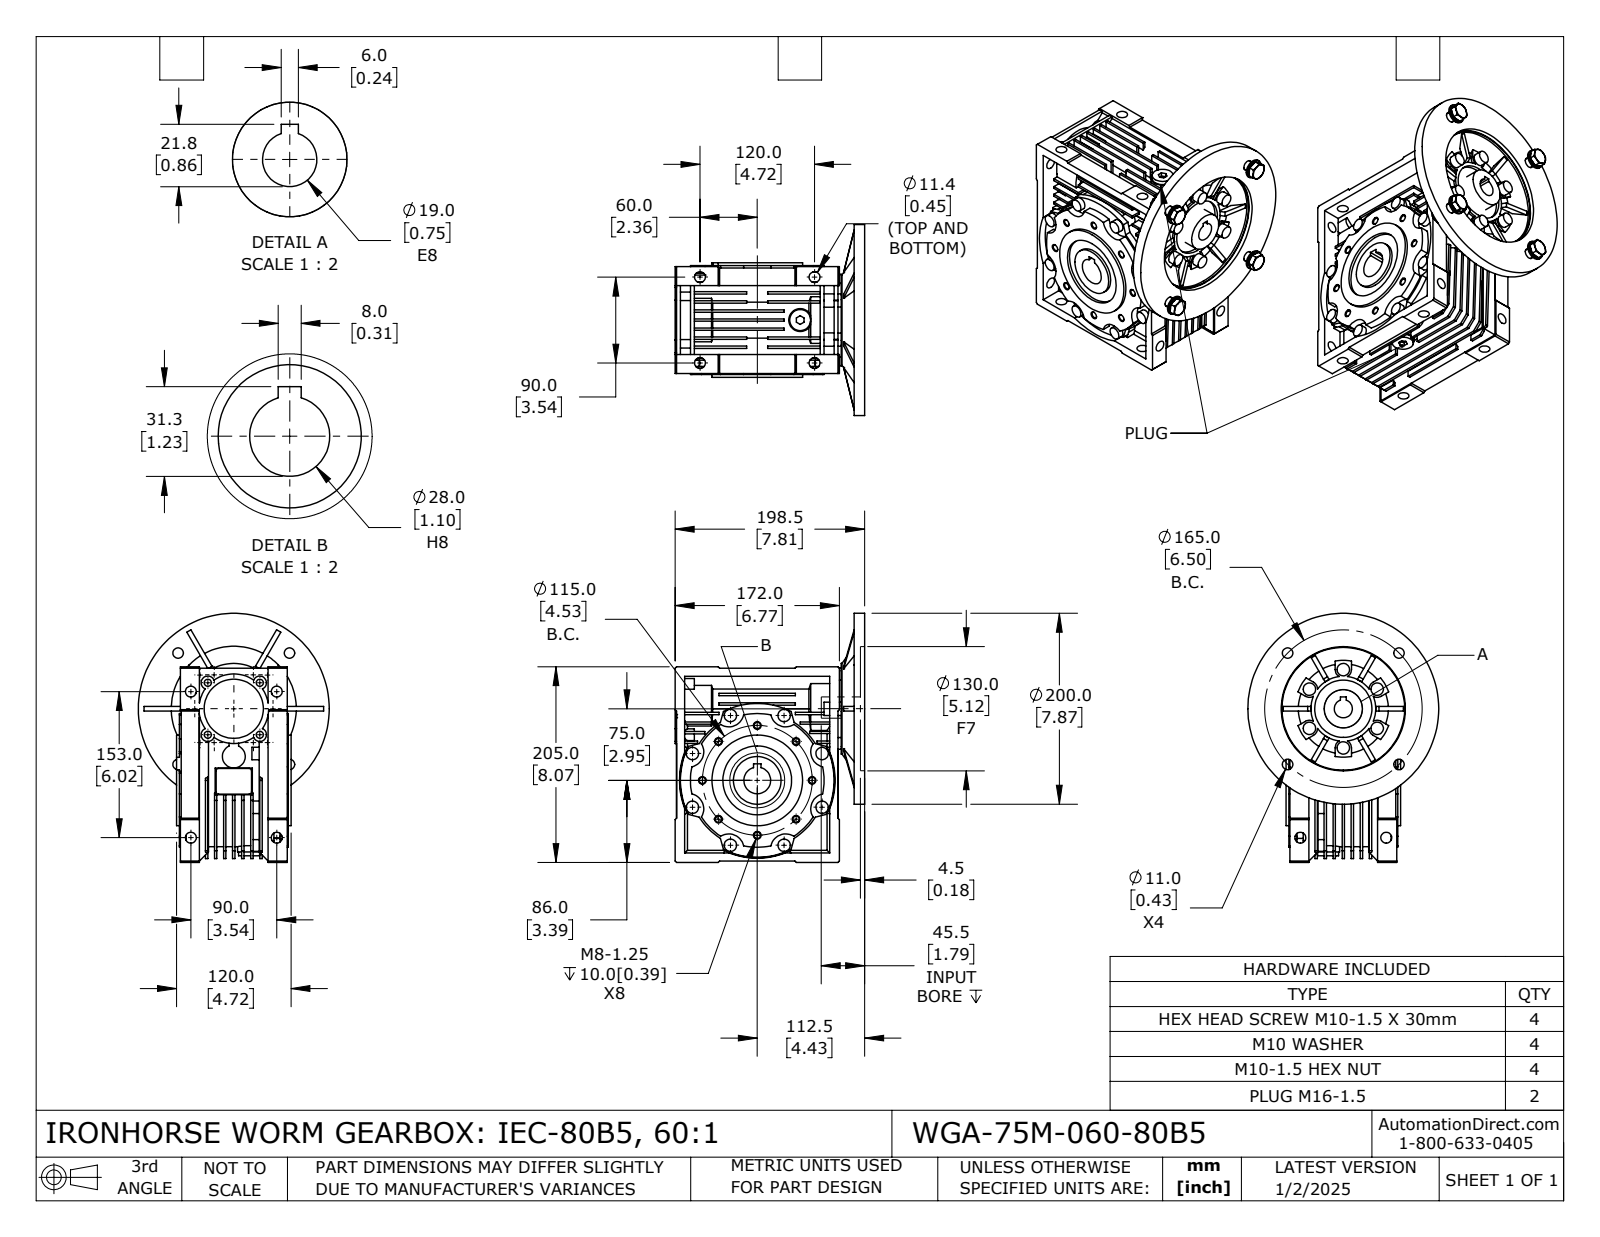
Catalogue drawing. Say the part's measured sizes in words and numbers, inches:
The part is named "WGA-75M-060-80B5". Its 3-D file was written by "SolidWorks 2024 (CONFIG_CONTROL_DESIGN)". It is 20 solids with 1447 faces: 790 planar, 439 cylindrical and 218 other. Overall it measures 10.276 by 8.462 by 7.874 inches. Its volume is 186.2 cubic inches and its surface area 831.4 square inches. Round holes: 8 of diameter 0.262, 8 of diameter 0.448, 4 of diameter 0.293, 4 of diameter 0.335, 4 of diameter 0.394, 4 of diameter 0.413, 4 of diameter 0.433, 2 of diameter 0.571, 1 of diameter 0.748, 1 of diameter 0.787, 1 of diameter 1.102, 1 of diameter 1.535. Round bosses or shafts: 14 of diameter 0.512, 4 of diameter 0.787, 4 of diameter 0.63, 3 of diameter 0.945, 2 of diameter 3.74, 2 of diameter 0.866, 2 of diameter 0.622, 2 of diameter 0.539. Partial cylindrical surfaces (rounded edges, fillets, slot ends): 10 of radius 0.276, 8 of radius 0.63, 6 of radius 0.335, 4 of radius 0.098, 1 of radius 1.338, 1 of radius 1.417, 1 of radius 1.437, 1 of radius 1.535. The main face-to-face distances are 0.374, 0.098, 0.748, 0.472, 0.276, 1.122, 0.65, 0.394, 1.093, 0.846. The hole center spacings are 1.733, 2.264, 3.202, 3.584, 4.183, 1.515, 2.143, 3.248.
